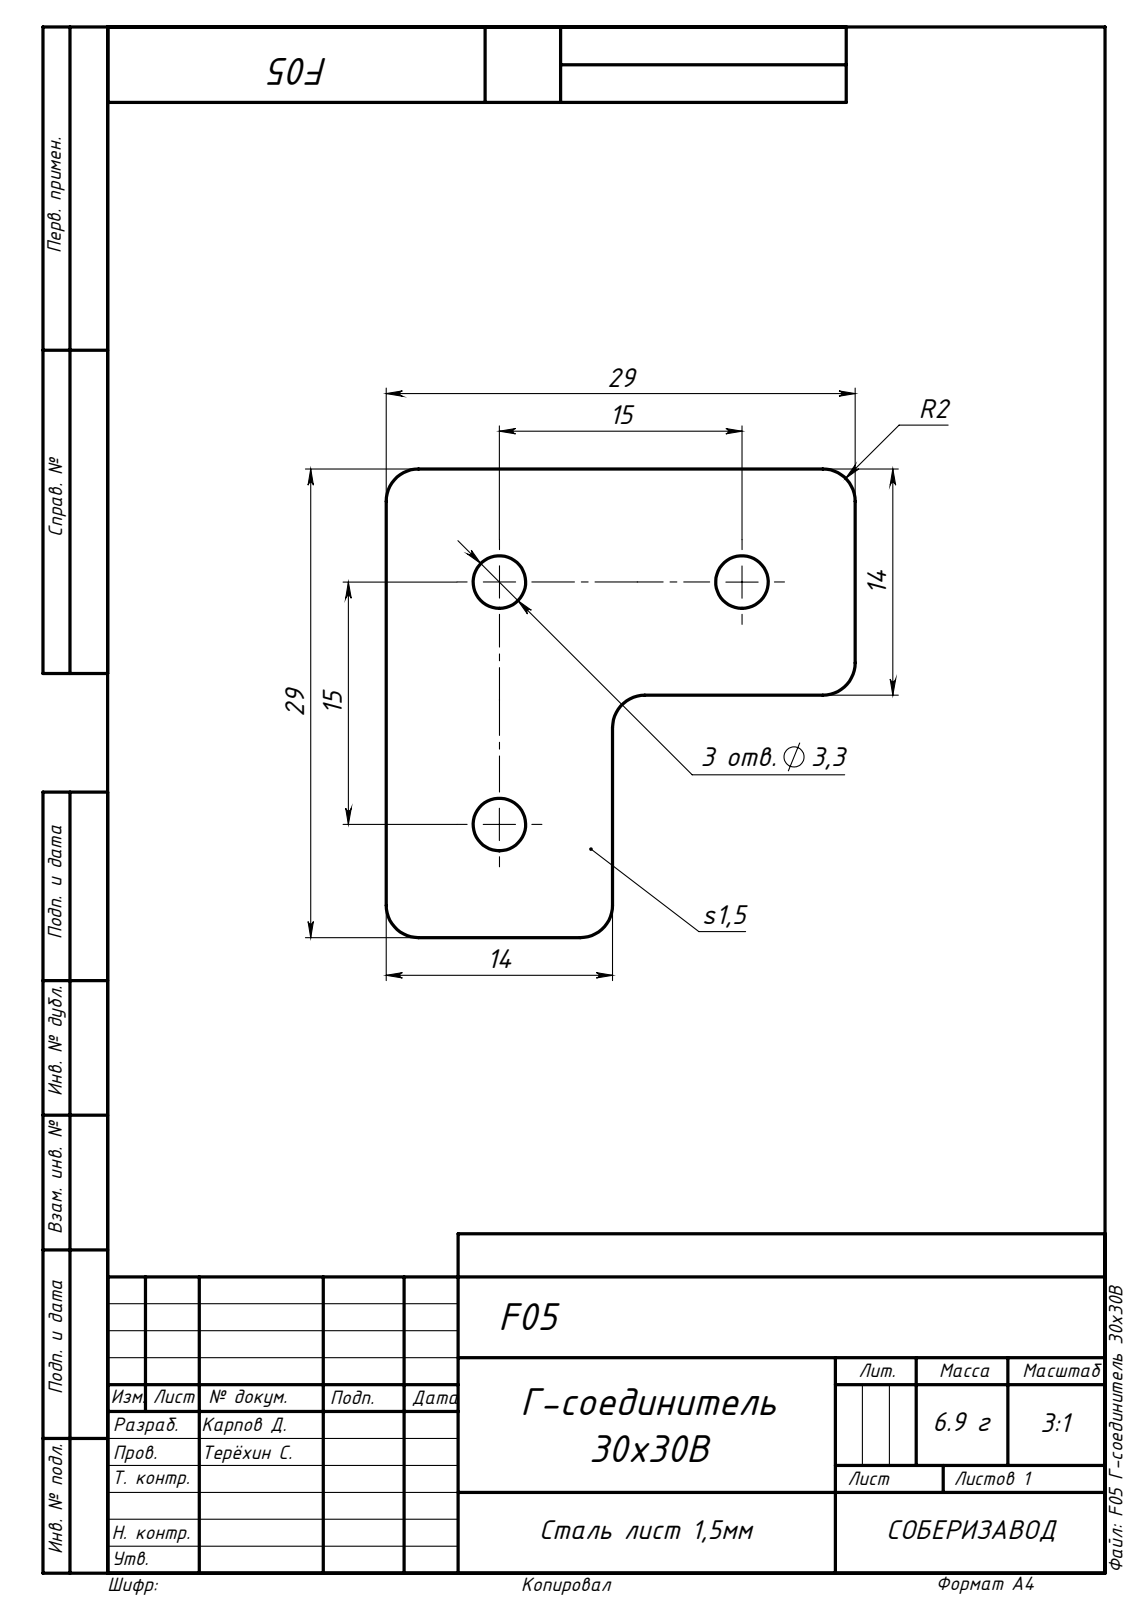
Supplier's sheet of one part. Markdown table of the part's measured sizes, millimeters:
| quantity | value |
| --- | --- |
| STEP written by | SolidWorks 2019 (AUTOMOTIVE_DESIGN) |
| units | millimeters |
| bodies | 1 solid, 20 faces (8 planar, 12 cylindrical, 0 other) |
| overall size | 29 × 29 × 1.5 |
| volume | 882 mm³ |
| surface area | 1 388 mm² |
| round holes (diameter × count) | 3.25 × 3 |
| partial cylindrical surfaces (radius × count) | 2 × 6 |
| main face-to-face distances | 1.5, 14, 29, 15 |
| hole center spacings | 15, 21.21 |
